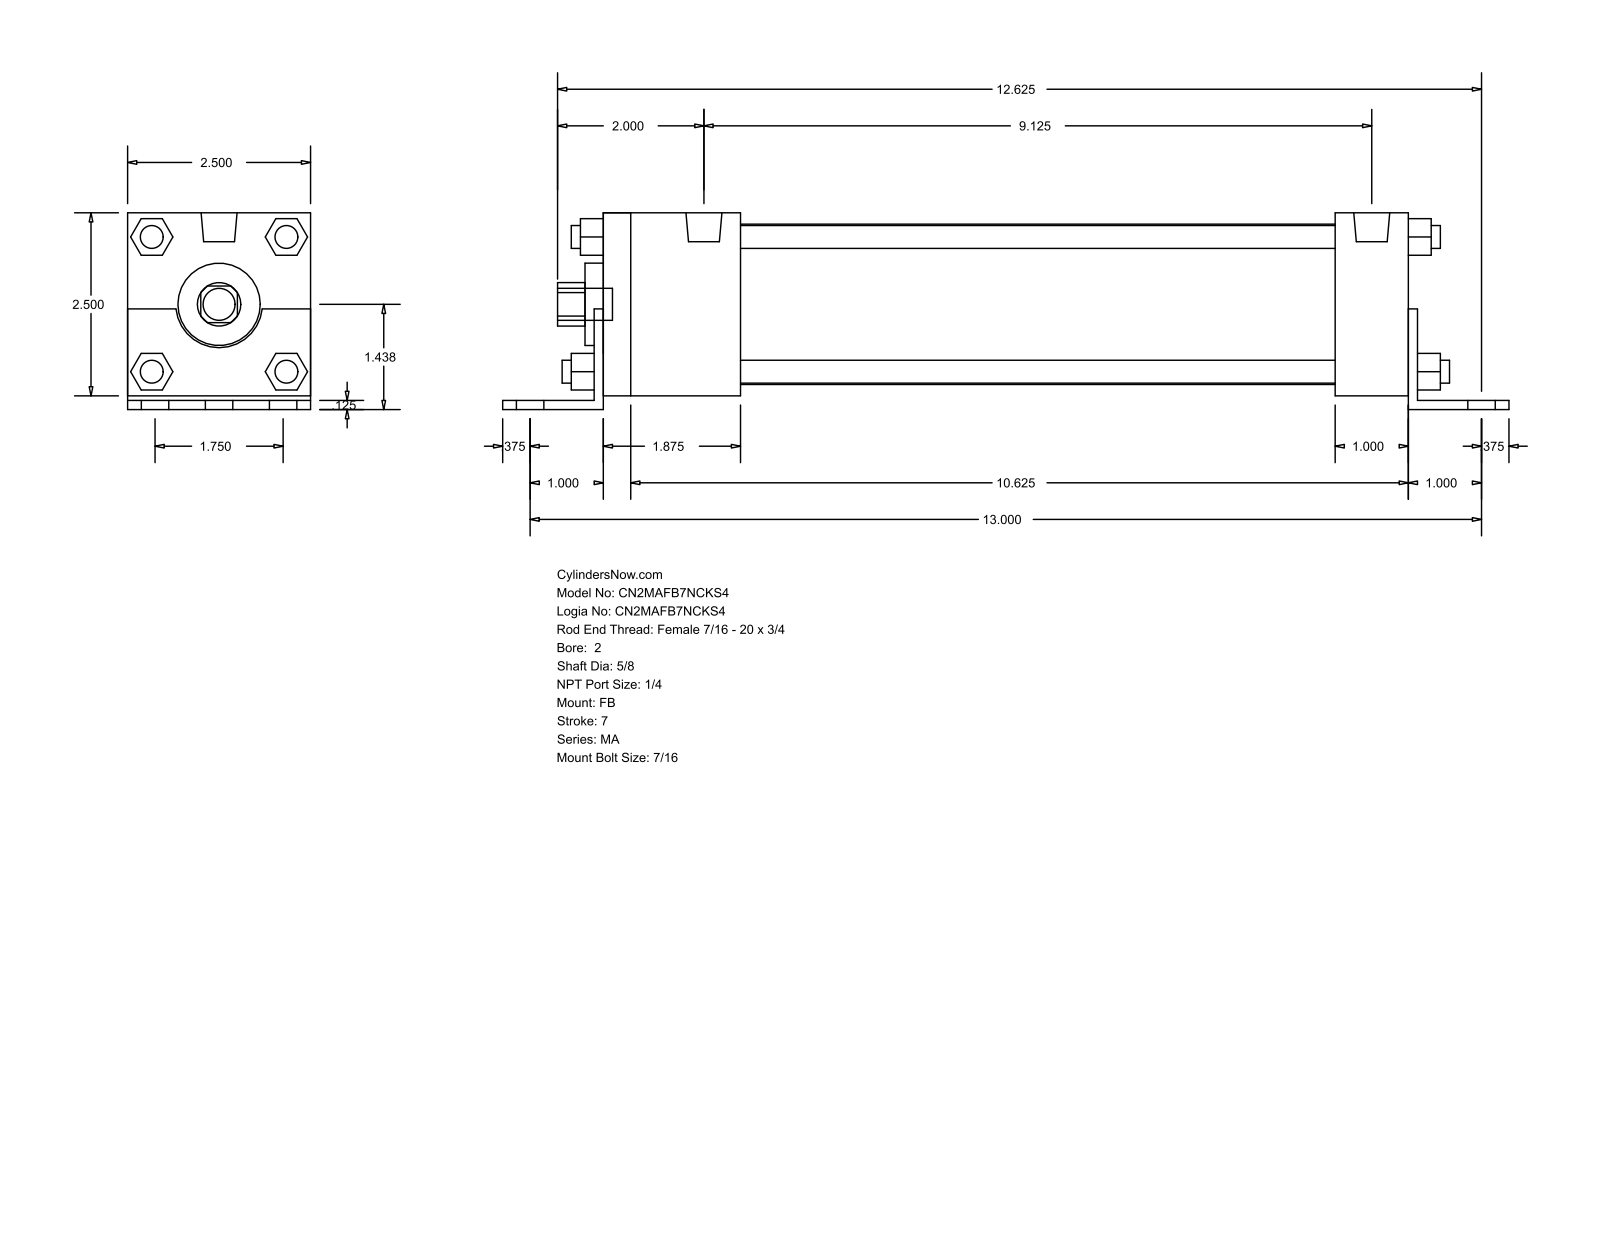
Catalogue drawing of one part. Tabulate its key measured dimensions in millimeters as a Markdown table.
| quantity | value |
| --- | --- |
| part name | MA_FB__0200_0.625 |
| STEP written by | GSSL Pune (CONFIG_CONTROL_DESIGN) |
| units | millimeters |
| bodies | 0 solids, 140 faces (105 planar, 35 cylindrical, 0 other) |
| overall size | 349.25 × 68.26 × 63.5 |
| round holes (diameter × count) | 15.88 × 1, 28.57 × 1, 55.63 × 1 |
| round bosses / shafts (diameter × count) | 7.94 × 8, 11.11 × 7, 12.49 × 2 |
| partial cylindrical surfaces (radius × count) | 7.54 × 1, 15.05 × 1 |
| main face-to-face distances | 63.5, 4.76, 3.17, 68.26, 1.59, 3.18, 65.09, 282.57, 279.39, 12.7 |
